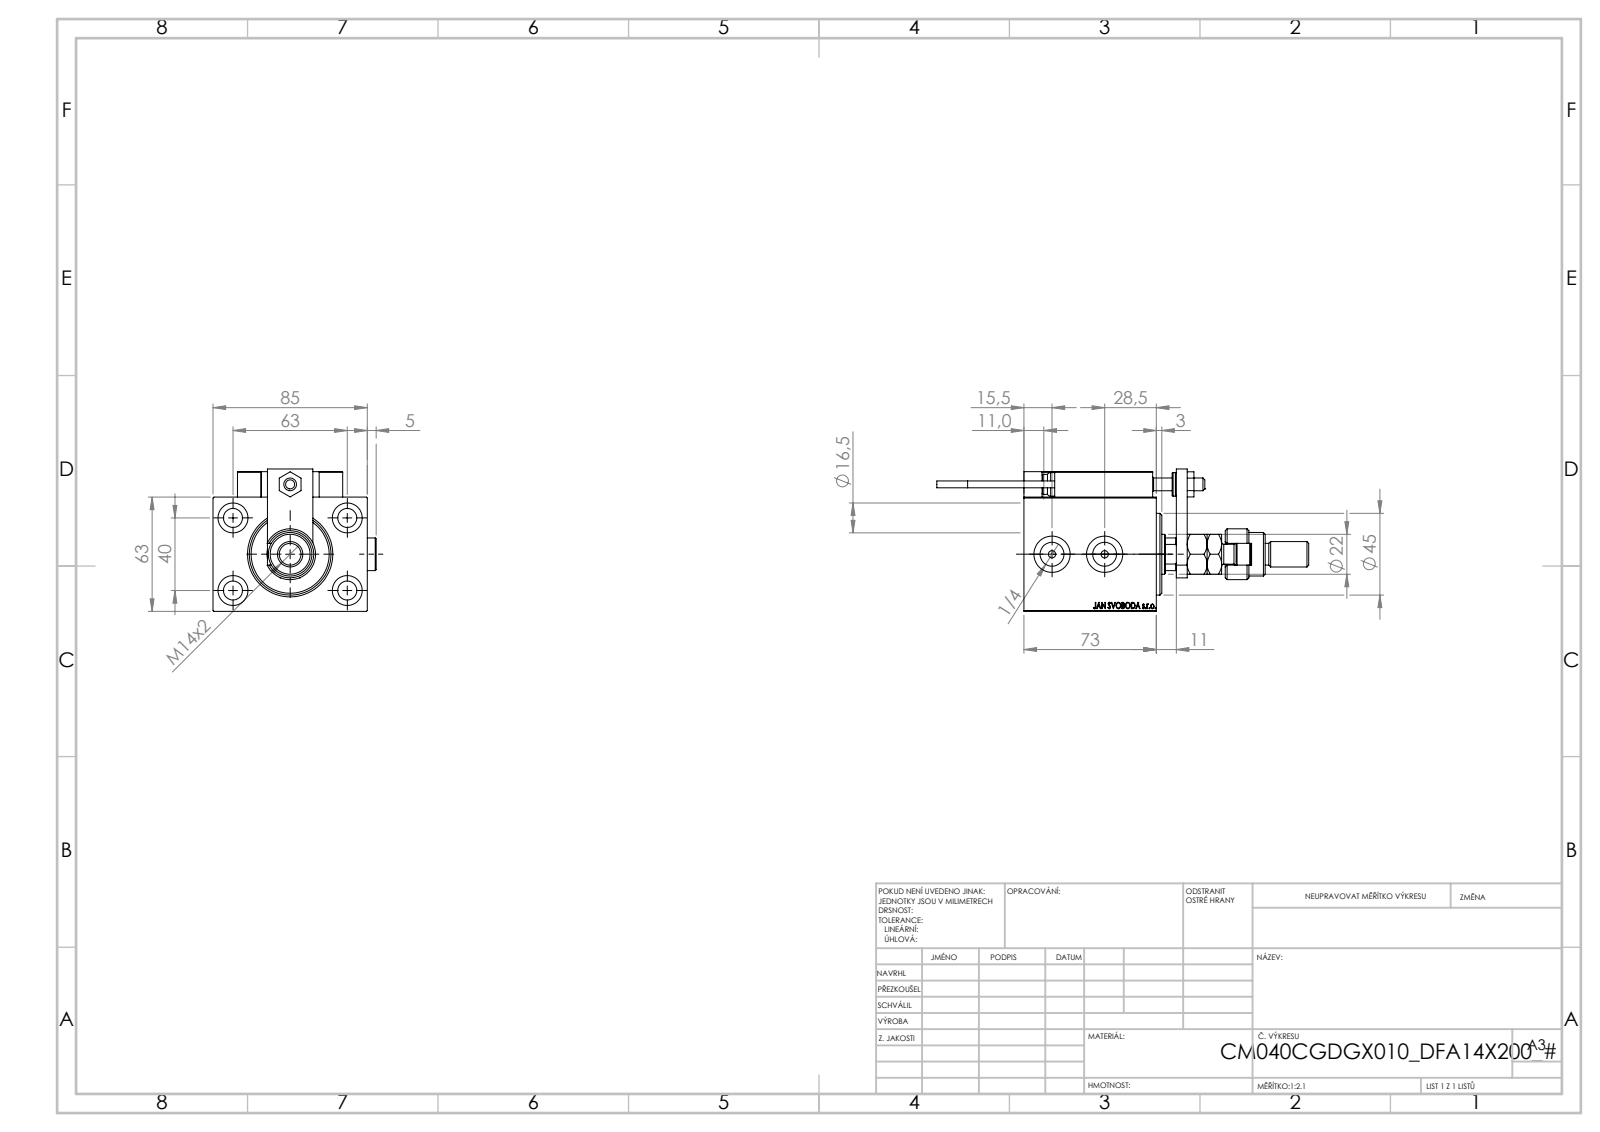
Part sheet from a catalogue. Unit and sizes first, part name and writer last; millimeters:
Units: millimetres
Overall size (bounding box): 205 × 89.9 × 78.5
Round holes (diameter × count): ⌀4 ×6, ⌀8 ×5, ⌀16.5 ×5, ⌀3.2 ×4, ⌀10.5 ×4, ⌀5 ×2, ⌀13.16 ×2, ⌀20 ×2, ⌀7 ×1, ⌀12.5 ×1, ⌀22 ×1, ⌀25.5 ×1
Round bosses / shafts (diameter × count): ⌀18 ×3, ⌀11 ×2, ⌀5 ×2, ⌀3.8 ×2, ⌀28 ×1, ⌀24 ×1, ⌀14 ×1, ⌀13 ×1
Partial cylindrical surfaces — rounded edges, fillets, slot ends (radius × count): R0.3 ×30, R3 ×2, R9.75 ×1, R10.5 ×1
Main face-to-face distances: 63, 22, 85, 14, 51, 73, 11, 62, 17, 77
Hole centre spacings: 37.31, 11.37, 20, 25.08, 29.59, 29.69, 33.3, 35.57
Volume: 414 139 mm³ · Surface area: 102 449 mm²
Bodies: 27 solids, 1419 faces (622 planar, 215 cylindrical, 582 other)
Part name (STEP PRODUCT): ZARAZKA; MFA; TYC_L79; KONCOVKA (+7 more)
STEP written by: SolidWorks 2019 (CONFIG_CONTROL_DESIGN)
